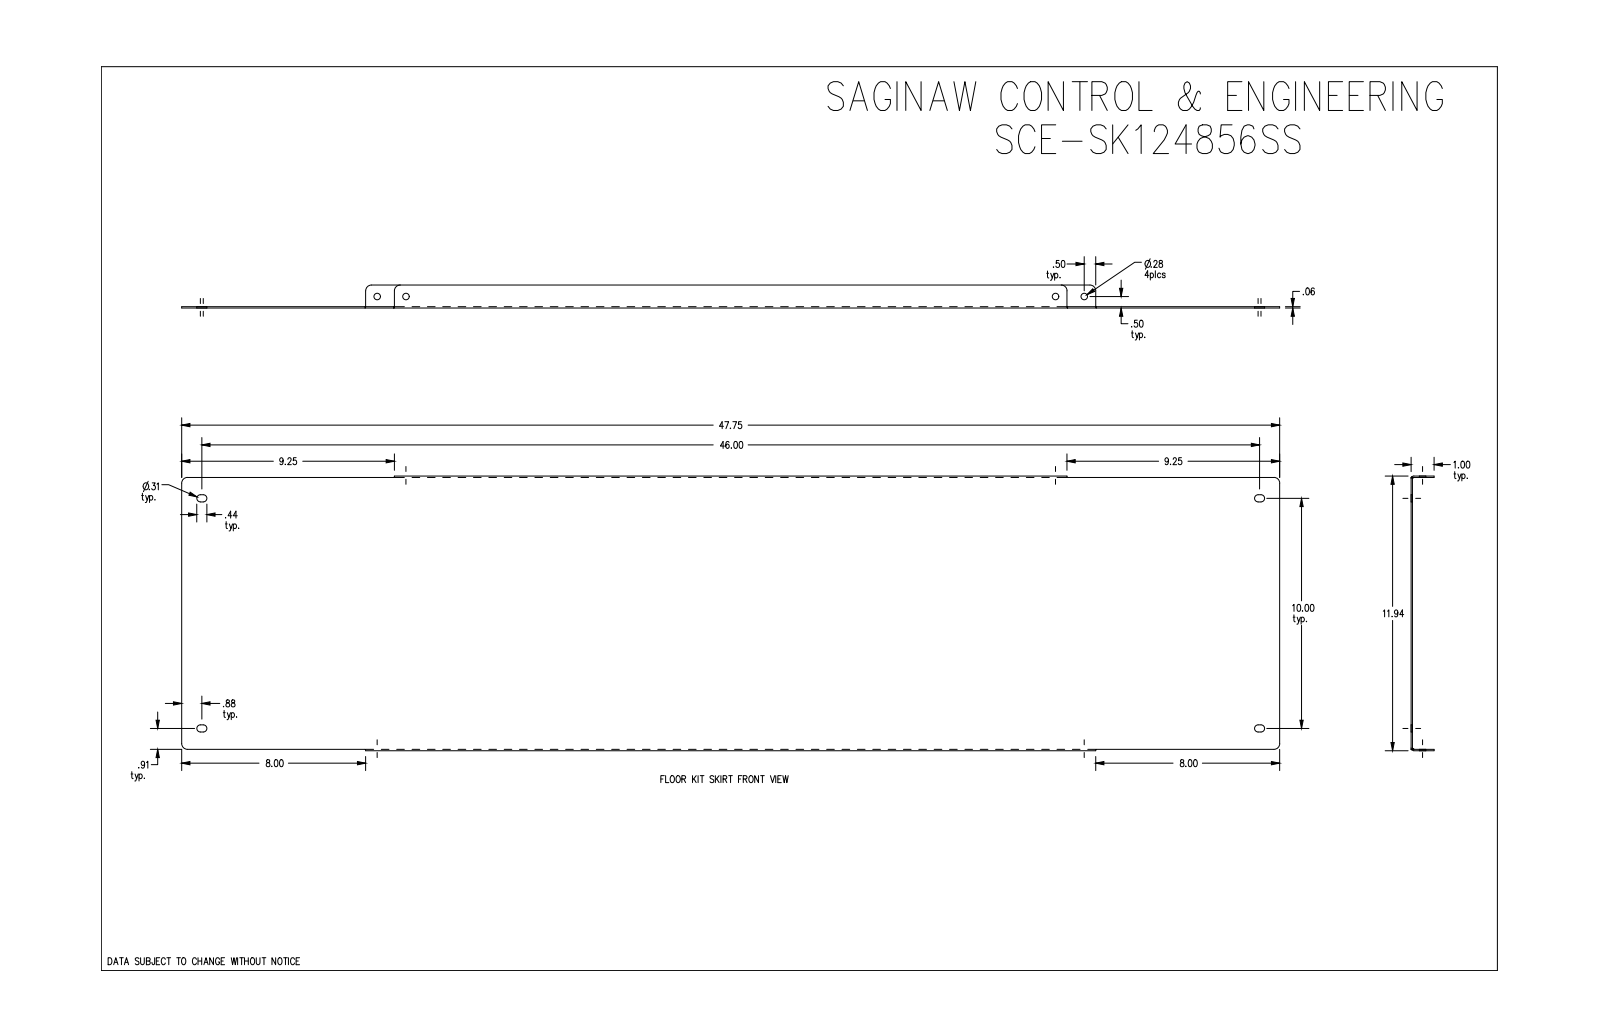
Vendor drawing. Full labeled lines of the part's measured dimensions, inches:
Part name (STEP PRODUCT): SCE-SK124856SS
STEP written by: SolidWorks 2019 (CONFIG_CONTROL_DESIGN)
Units: inches
Bodies: 1 solid, 62 faces (26 planar, 24 cylindrical, 12 other)
Overall size (bounding box): 47.75 × 11.938 × 1
Volume: 37.33 in³ · Surface area: 1 252 in²
Round holes (diameter × count): ⌀0.281 ×4
Partial cylindrical surfaces — rounded edges, fillets, slot ends (radius × count): R0.156 ×8, R0.25 ×8, R0.06 ×2, R0.12 ×2
Main face-to-face distances: 0.06, 0.06, 11.878, 11.817, 11.938, 0.94, 1, 47.75, 9.25, 38.5
Hole centre spacings: 1.25, 29.5, 28.25, 30.75
